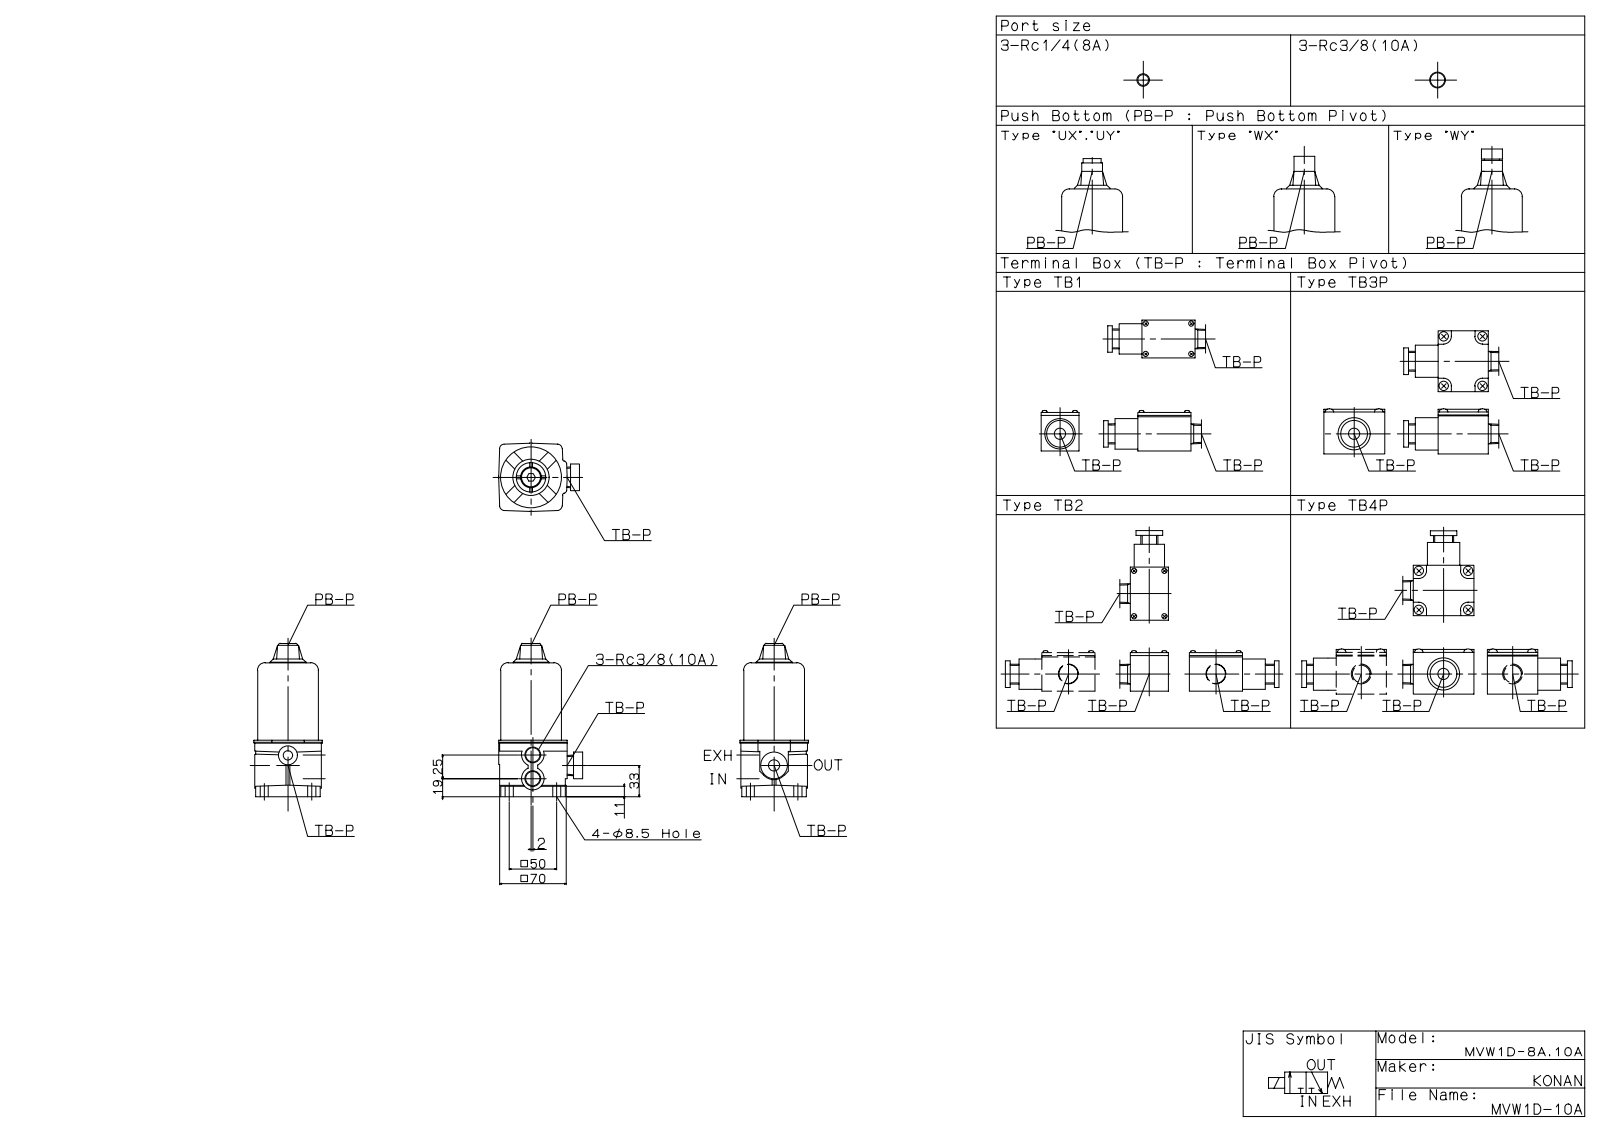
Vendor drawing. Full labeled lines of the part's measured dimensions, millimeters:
Part name (STEP PRODUCT): MVW1D-10A
STEP written by: SolidWorks 2023 (AUTOMOTIVE_DESIGN)
Units: millimetres
Bodies: 1 solid, 85 faces (43 planar, 42 cylindrical, 0 other)
Overall size (bounding box): 161.5 × 88 × 72
Volume: 475 057 mm³ · Surface area: 54 155 mm²
Round holes (diameter × count): ⌀17.3 ×3
Round bosses / shafts (diameter × count): ⌀22 ×2, ⌀64 ×1, ⌀37.5 ×1, ⌀28 ×1, ⌀24 ×1
Partial cylindrical surfaces — rounded edges, fillets, slot ends (radius × count): R5 ×8, R8 ×4, R7 ×1, R10 ×1, R12 ×1, R14 ×1, R15 ×1
Main face-to-face distances: 11, 46, 35, 70, 141, 130, 95, 24, 59.5, 48.5
Hole centre spacings: 11, 14, 25
